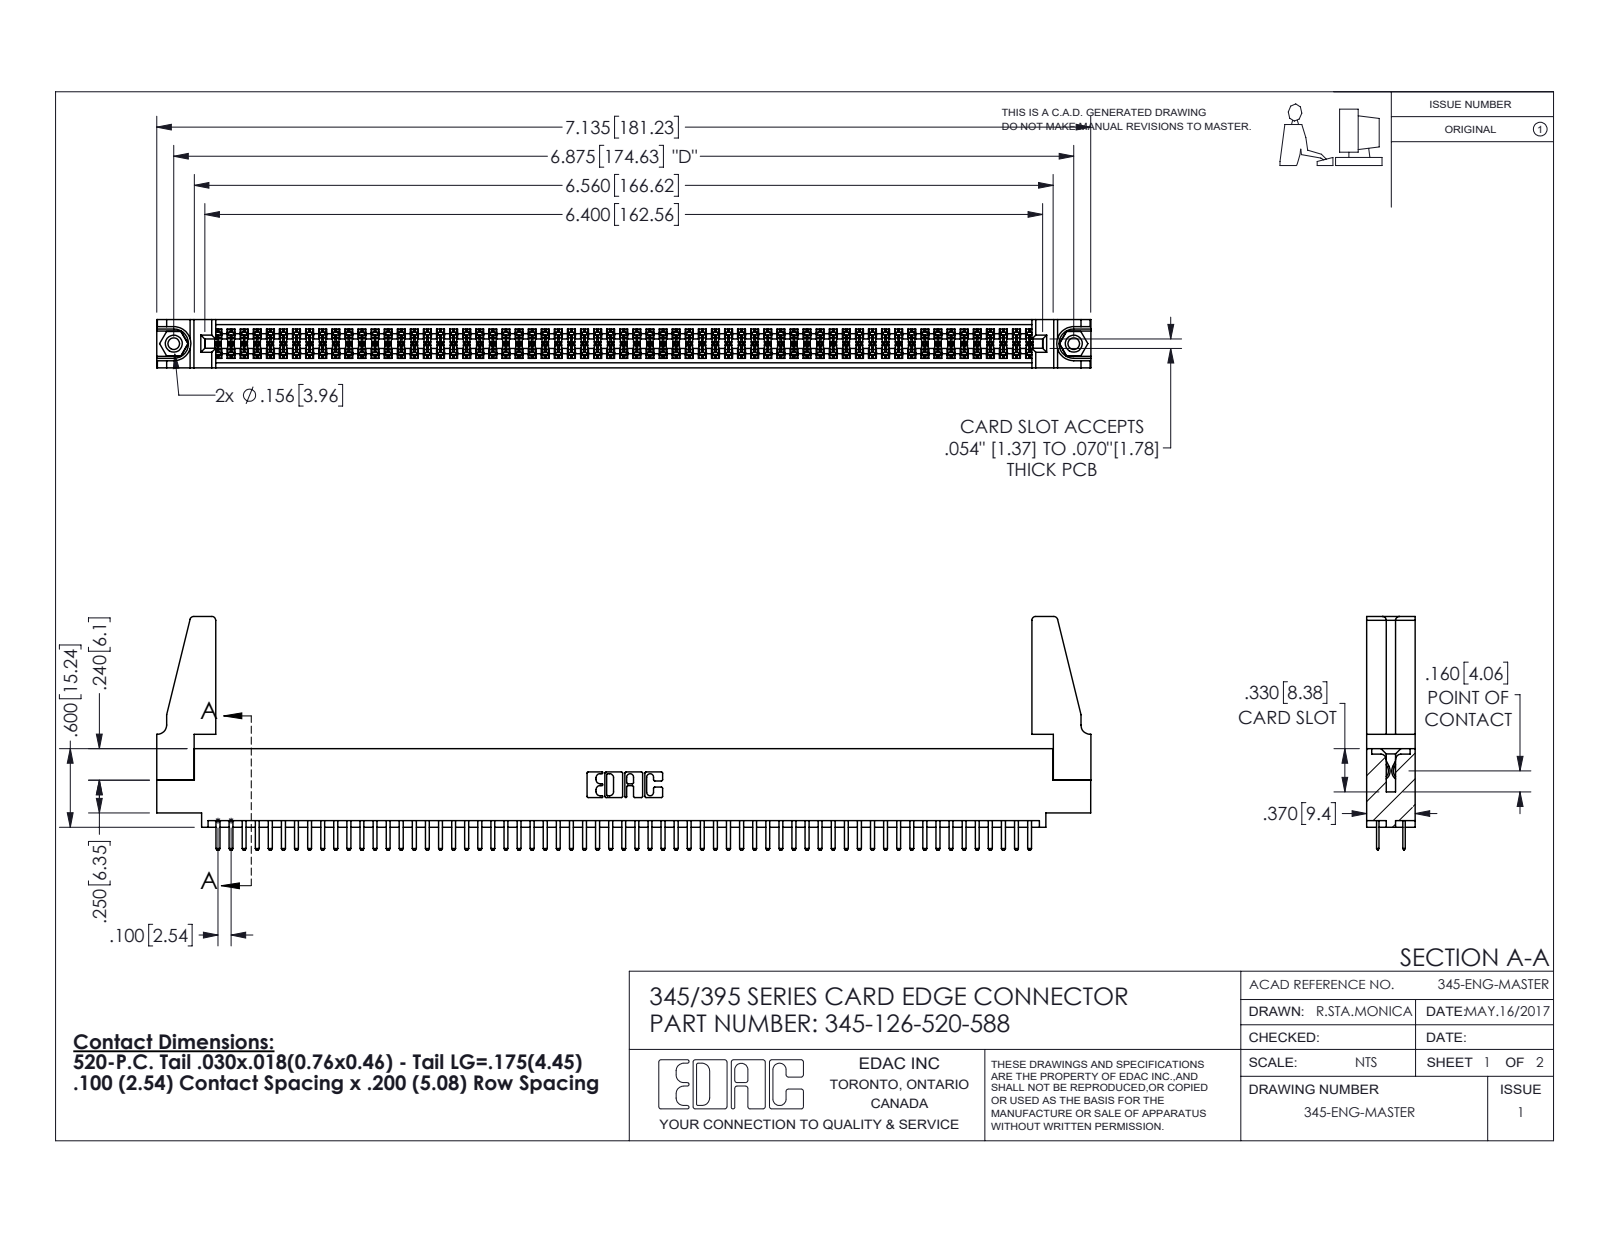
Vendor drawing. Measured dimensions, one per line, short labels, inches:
name: 345-250-001_345-250-001-102; 345-292-001_345-293-120; 345-220-078_345-220-088; 345-126-520-588 (+1 more)
written by: SolidWorks 2016 (CONFIG_CONTROL_DESIGN)
unit: in
bodies: 131 solids, 7058 faces (4566 planar, 2476 cylindrical, 16 other)
size: 7.136 × 1.785 × 0.37
volume: 1.277 in³; area: 45.92 in²
holes: 2× ⌀0.089, 2× ⌀0.125, 2× ⌀0.156, 1× ⌀0.064
bosses: 2× ⌀0.155
rounds: 189× R0.006, 130× R0.01, 22× R0.01, 8× R0.03, 6× R0.007, 6× R0.031, 3× R0.026, 2× R0.014
face distances: 0.072, 0.298, 0.37, 0.2, 0.098, 0.272, 0.025, 0.225, 0.022, 0.072
hole spacings: 0.27, 6.639, 6.875
